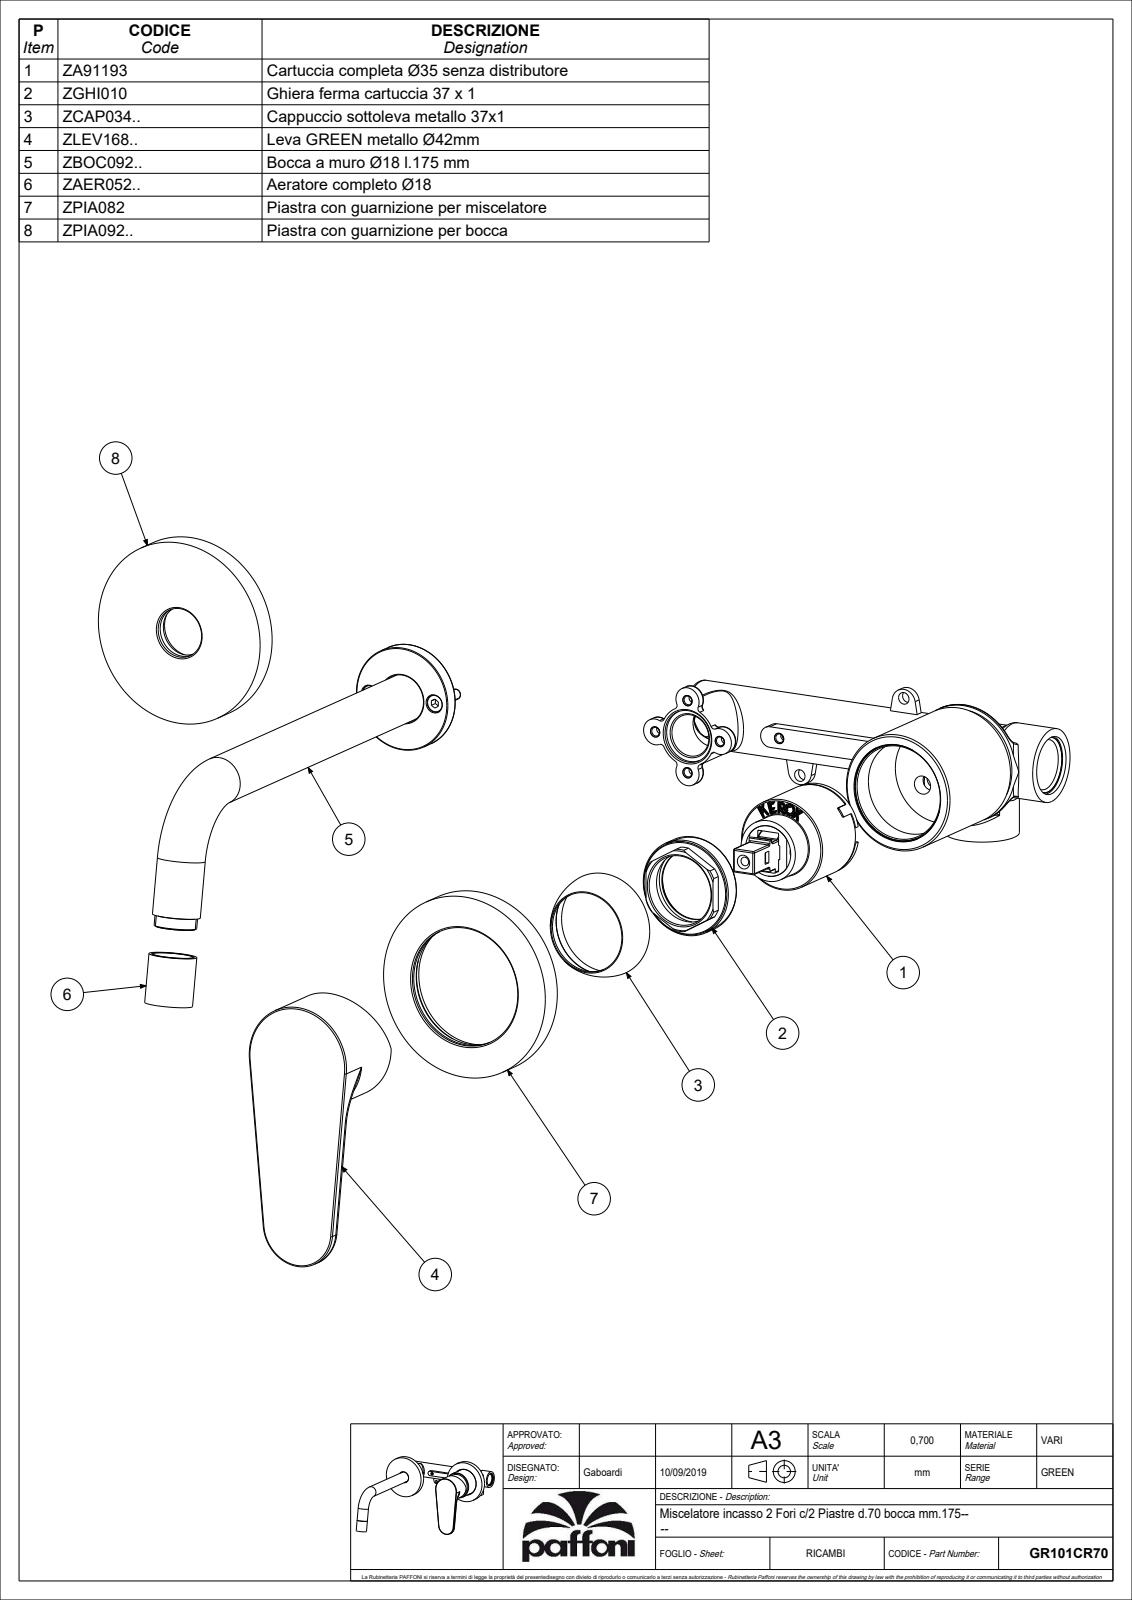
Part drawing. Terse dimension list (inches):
name: GR101CR70
written by: CREO PARAMETRIC BY PTC INC, 2020044 (CONFIG_CONTROL_DESIGN)
unit: in
bodies: 3 solids, 107 faces (45 planar, 41 cylindrical, 21 other)
size: 7.188 × 7.047 × 4.508
volume: 11.45 in³; area: 80.31 in²
holes: 1× ⌀0.118, 1× ⌀0.165, 1× ⌀1.535
bosses: 2× ⌀2.756, 2× ⌀0.709, 1× ⌀1.764, 1× ⌀1.654, 1× ⌀0.299, 1× ⌀0.217
rounds: 2× R0.02, 2× R0.118, 1× R0.591
face distances: 0.354, 2.618, 2.264, 0.236, 2.382, 2.028, 0.098, 0.138, 2.52, 2.165
